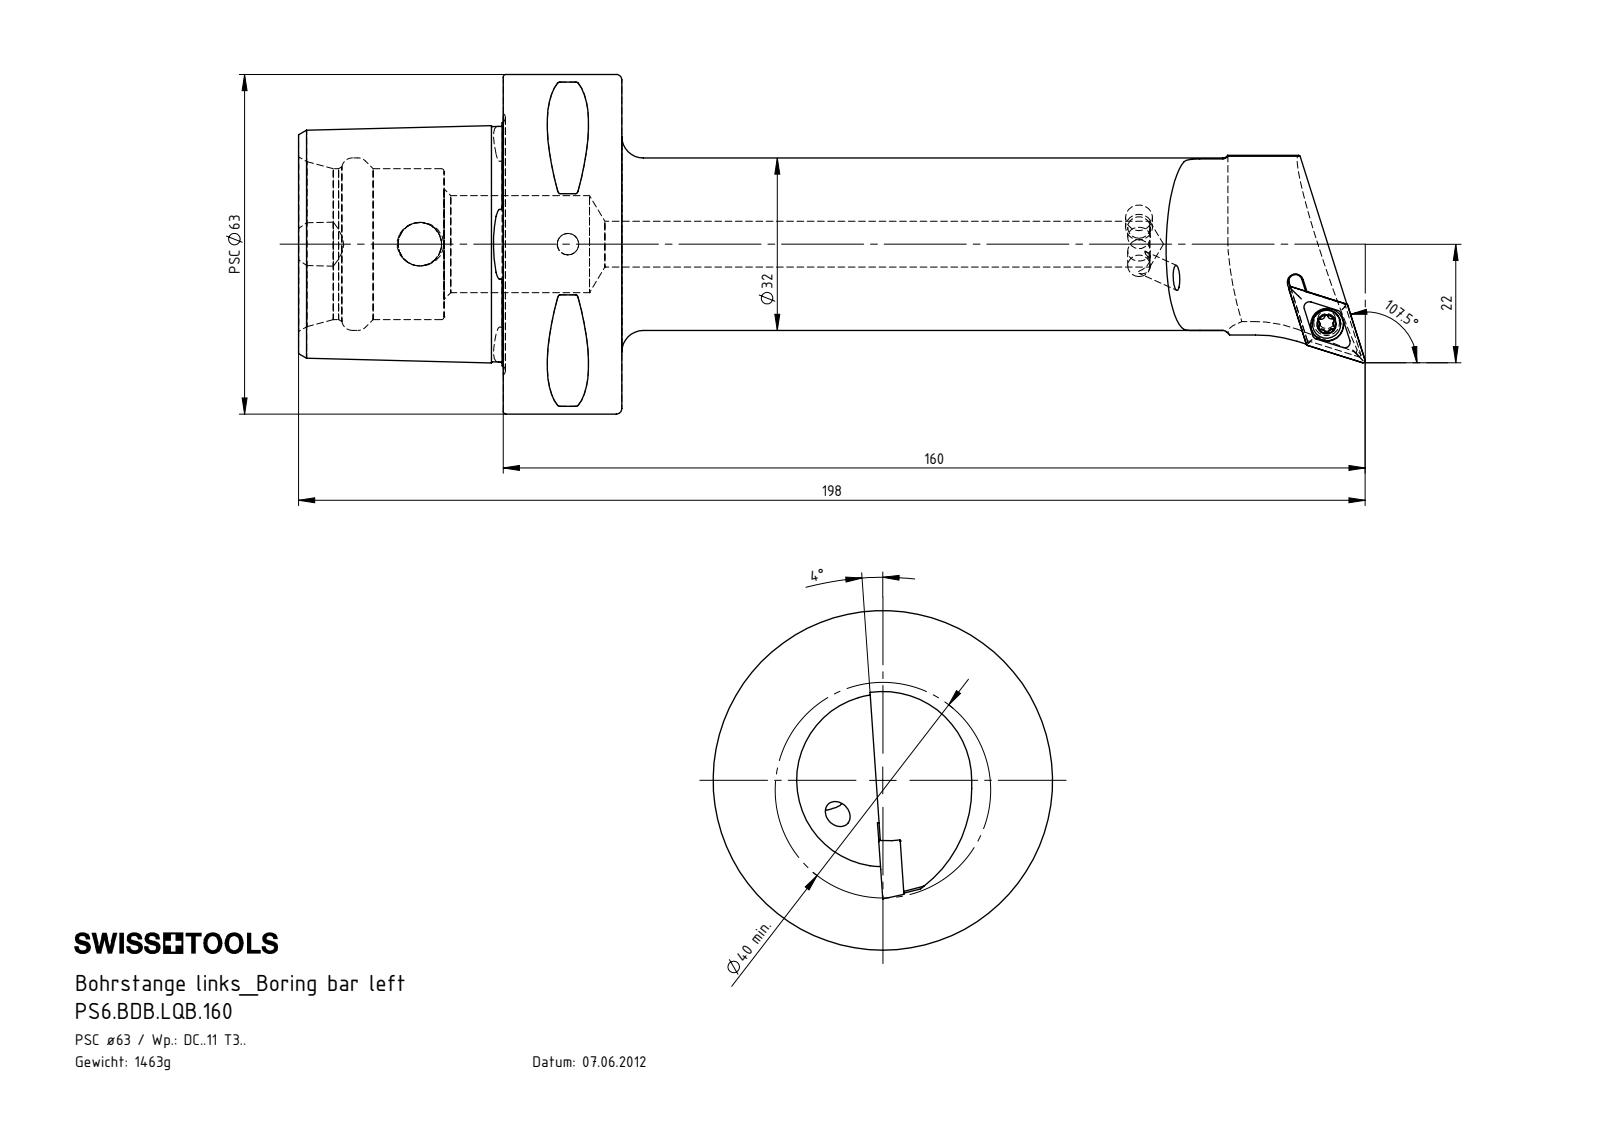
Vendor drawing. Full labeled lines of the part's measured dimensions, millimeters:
Part name (STEP PRODUCT): DCMT11T304; PS6-BDB.LQB.160; PS6-BDB.LQB.160_A; WCB-ER2.001.009_A (+1 more)
STEP written by: SolidWorks 2012 (CONFIG_CONTROL_DESIGN)
Units: millimetres
Bodies: 5 solids, 289 faces (53 planar, 75 cylindrical, 161 other)
Overall size (bounding box): 198 × 63 × 63
Volume: 186 085 mm³ · Surface area: 36 526 mm²
Round holes (diameter × count): ⌀4 ×2, ⌀4.2 ×2, ⌀3.3 ×1, ⌀4.4 ×1, ⌀6.1 ×1, ⌀8.1 ×1, ⌀8.5 ×1, ⌀18 ×1, ⌀28 ×1, ⌀32 ×1
Round bosses / shafts (diameter × count): ⌀63 ×1, ⌀5.25 ×1, ⌀5 ×1, ⌀4 ×1
Partial cylindrical surfaces — rounded edges, fillets, slot ends (radius × count): R0.5 ×8, R0.34 ×6, R0.59 ×6, R1.25 ×1, R3 ×1, R6 ×1, R16.5 ×1, R23 ×1
Main face-to-face distances: 22, 38, 60, 24.88, 27, 11, 33, 55.8, 3.67, 37.8
Hole centre spacings: 27.5
